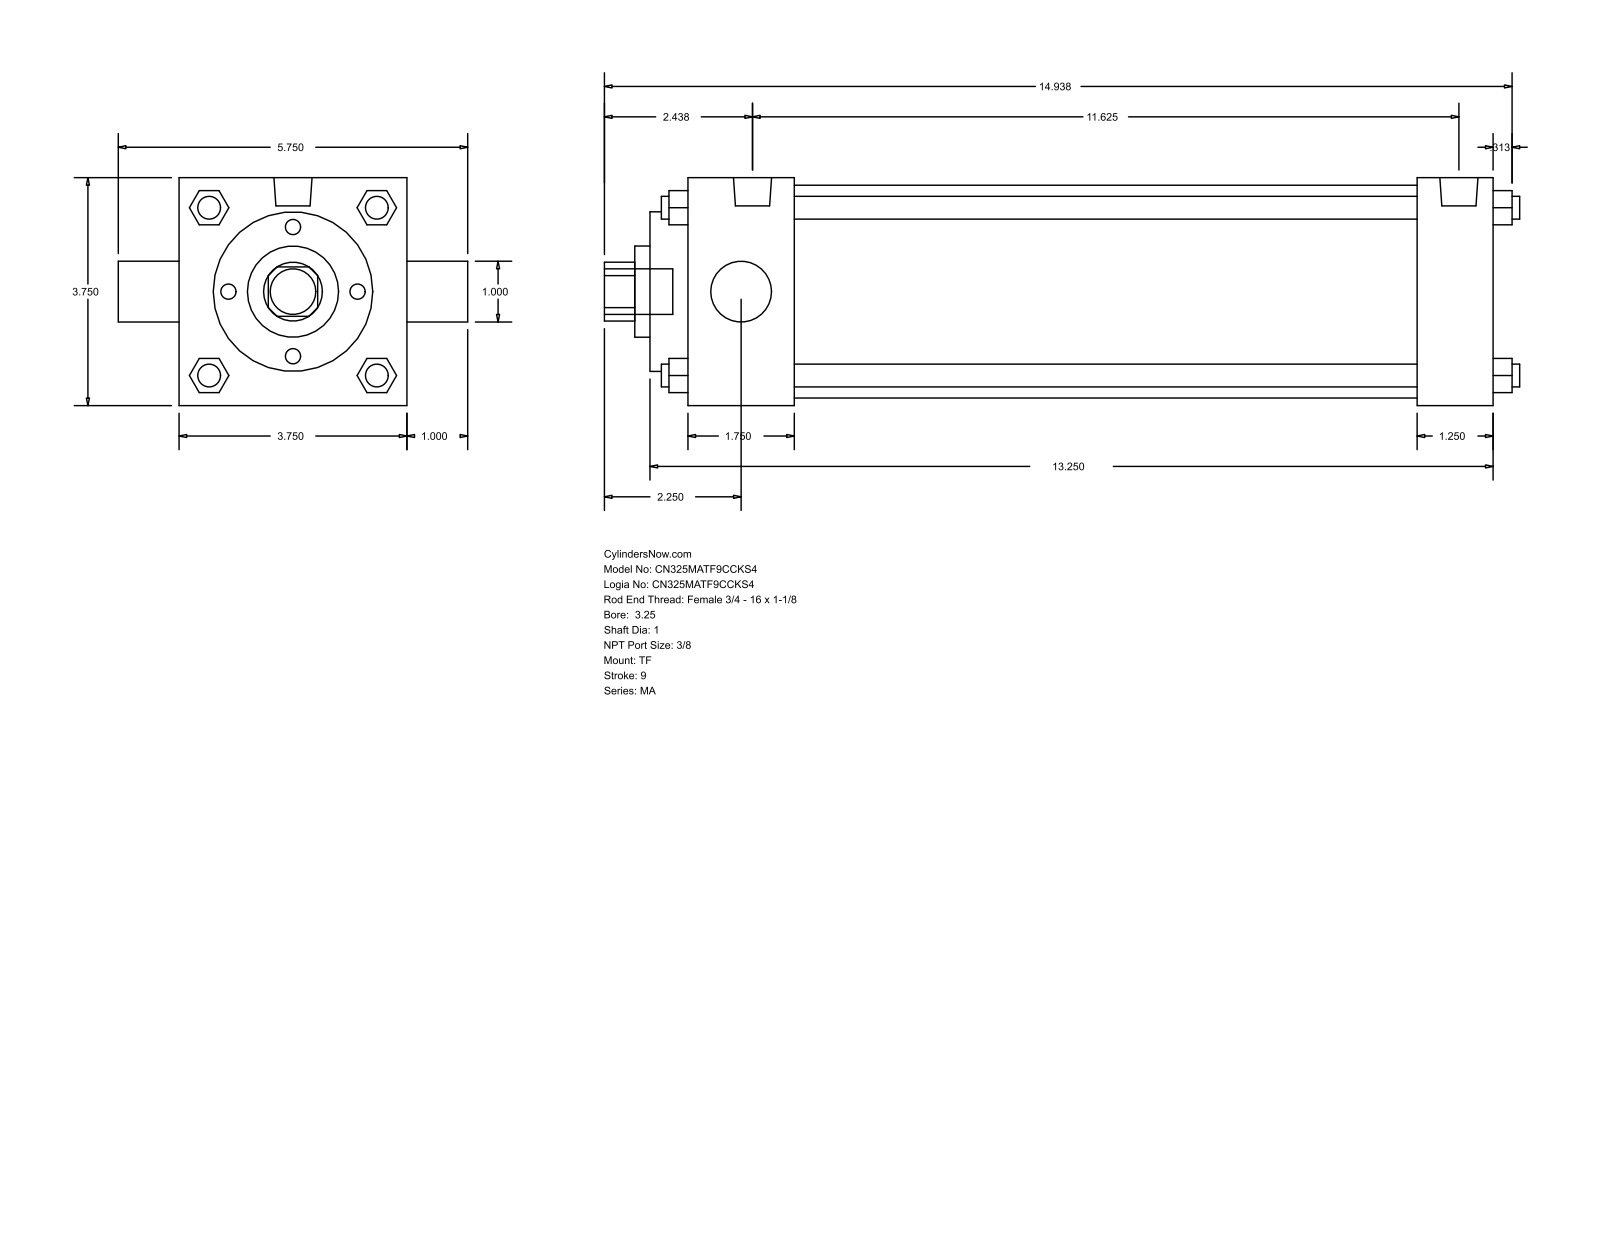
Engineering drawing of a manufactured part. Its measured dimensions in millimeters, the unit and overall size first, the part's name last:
Units: millimetres
Overall size (bounding box): 382.59 × 146.05 × 95.25
Round holes (diameter × count): ⌀25.4 ×2, ⌀38.1 ×1, ⌀66.67 ×1, ⌀88.9 ×1
Round bosses / shafts (diameter × count): ⌀9.53 ×4, ⌀11.11 ×3, ⌀15.93 ×2, ⌀19.05 ×1
Partial cylindrical surfaces — rounded edges, fillets, slot ends (radius × count): R12.29 ×1
Main face-to-face distances: 95.24, 336.56, 15.87, 44.46, 304.81, 260.35, 292.1, 31.75, 60.33, 320.68
Bodies: 0 solids, 122 faces (93 planar, 29 cylindrical, 0 other)
Part name (STEP PRODUCT): MA_TF__0325_1
STEP written by: GSSL Pune (CONFIG_CONTROL_DESIGN)
